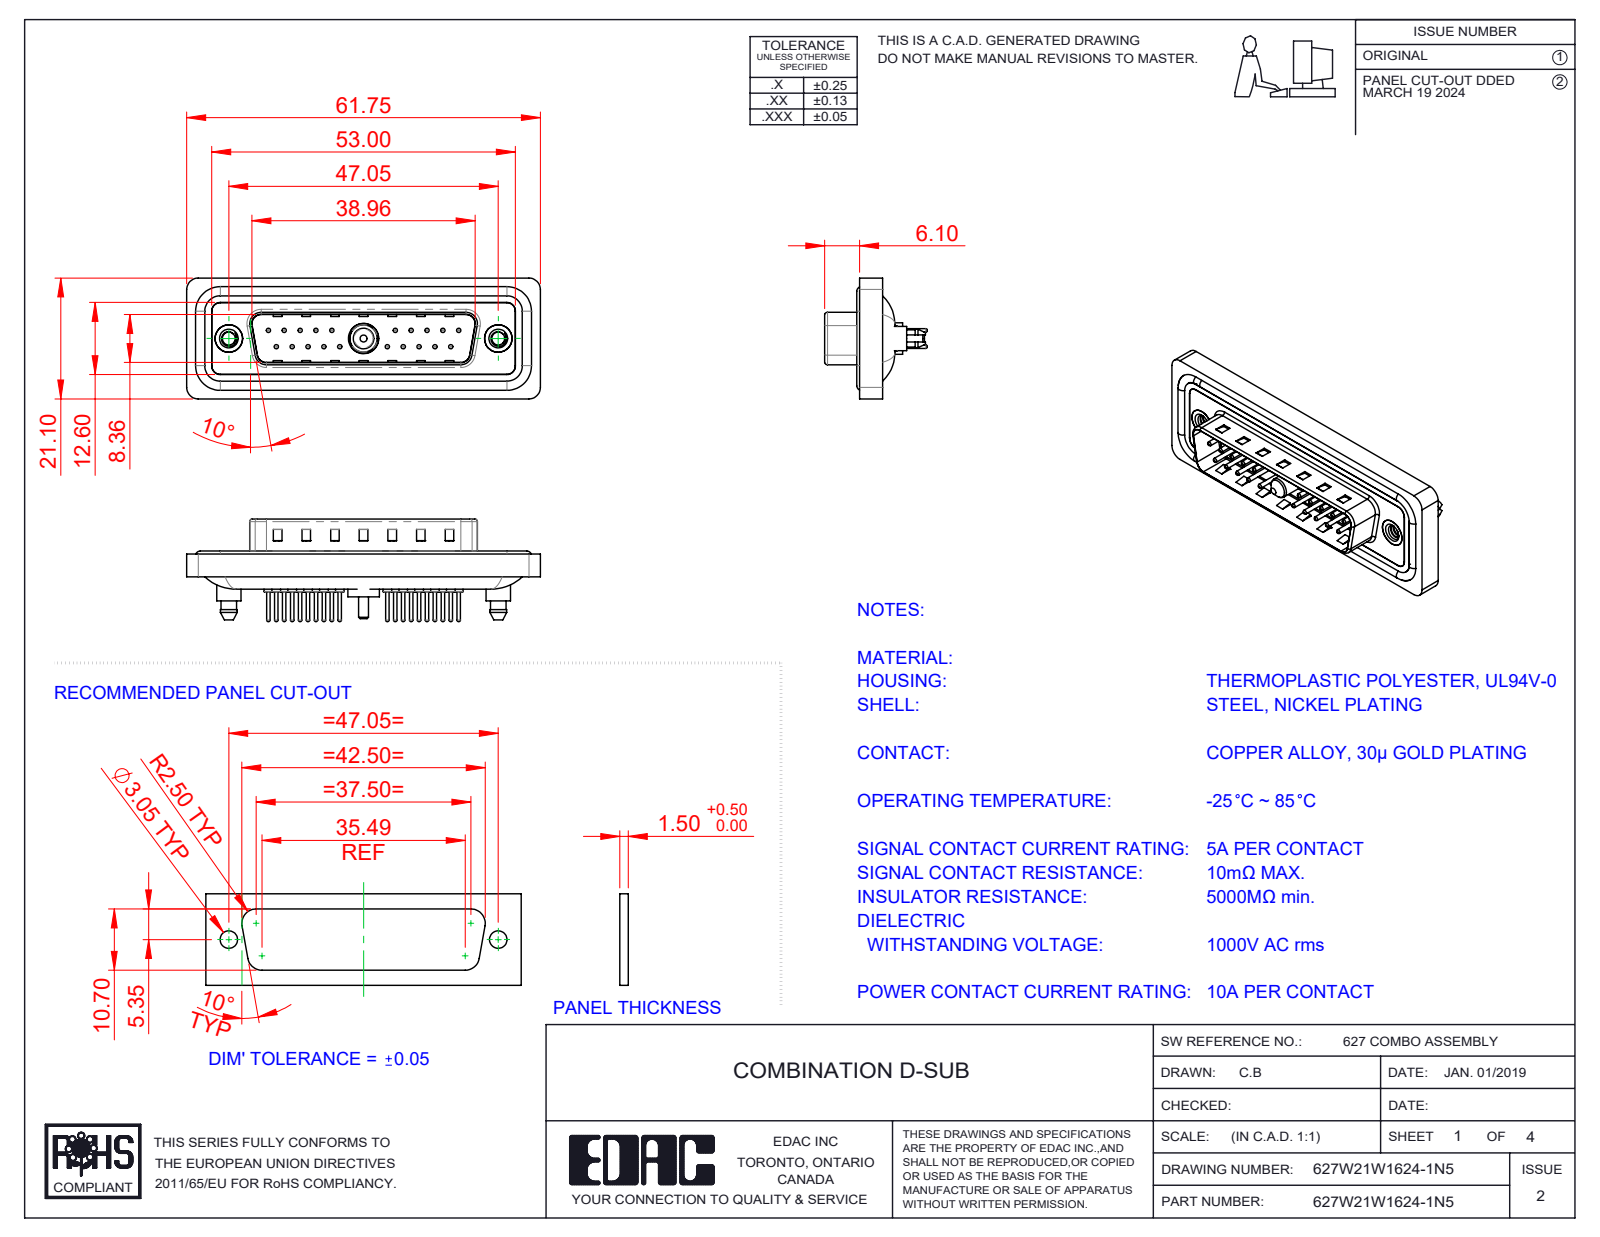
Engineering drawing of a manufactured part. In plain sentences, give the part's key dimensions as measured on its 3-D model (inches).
The part is named "Power Pin_10A S; 627Combo Housing_21W1; 627Combo Contact Row 1_24; 627Combo Shell Rear_25 Contacts (+5 more)". Its 3-D file was written by "SolidWorks 2023 (CONFIG_CONTROL_DESIGN)". It is 29 solids with 1312 faces: 375 planar, 519 cylindrical and 418 other. Overall it measures 2.431 by 0.831 by 0.705 inches. Its volume is 0.447 cubic inches and its surface area 19.02 square inches. Round holes: 20 of diameter 0.03, 20 of diameter 0.063, 20 of diameter 0.079, 2 of diameter 0.089, 2 of diameter 0.157, 2 of diameter 0.189, 2 of diameter 0.197, 1 of diameter 0.191, 1 of diameter 0.209. Round bosses or shafts: 20 of diameter 0.059, 20 of diameter 0.024, 4 of diameter 0.063, 2 of diameter 0.213, 2 of diameter 0.193, 2 of diameter 0.167, 1 of diameter 0.217, 1 of diameter 0.205. Partial cylindrical surfaces (rounded edges, fillets, slot ends): 24 of radius 0.059, 18 of radius 0.079, 10 of radius 0.063, 8 of radius 0.02, 4 of radius 0.01, 4 of radius 0.024, 4 of radius 0.026, 4 of radius 0.035. The main face-to-face distances are 0.016, 0.059, 0.043, 0.063, 0.02, 0.122, 0.114, 0.161, 0.032, 0.377. The hole center spacings are 0.124, 0.109, 0.218, 0.327, 0.198, 0.763, 0.826, 0.872.
